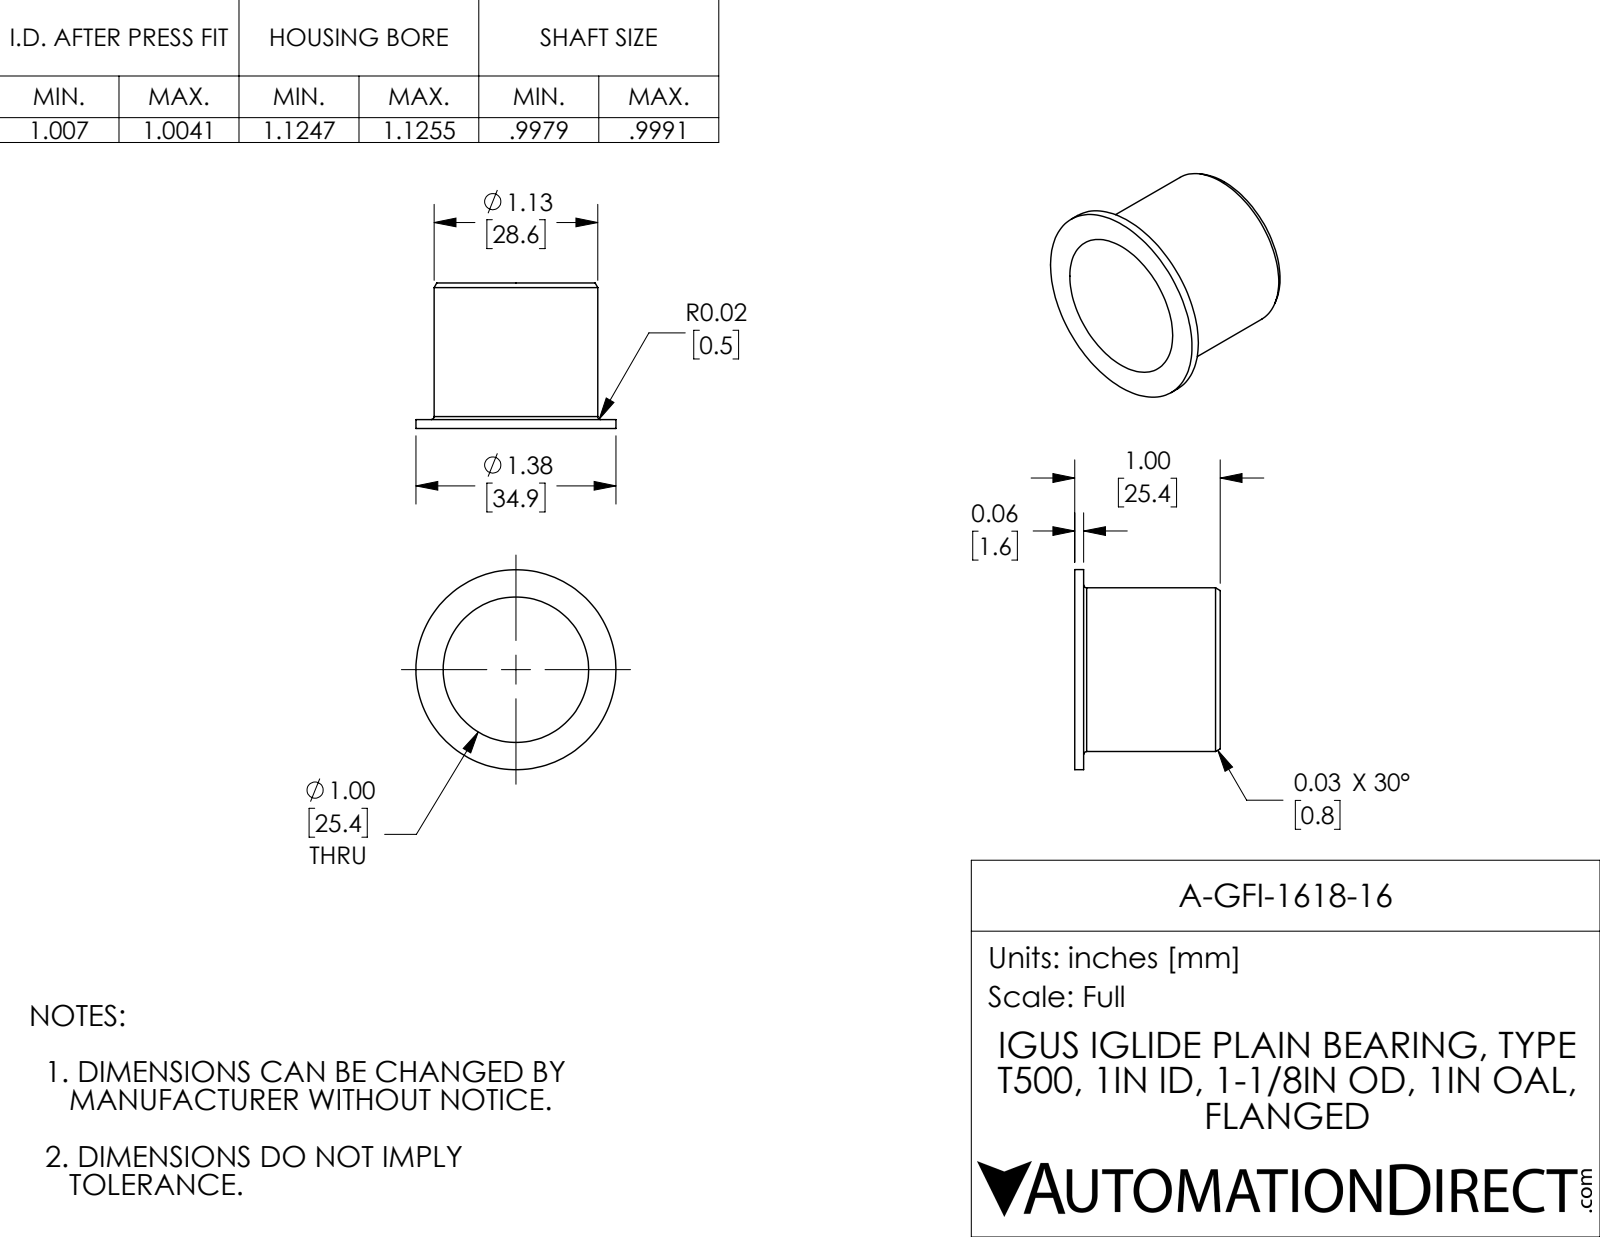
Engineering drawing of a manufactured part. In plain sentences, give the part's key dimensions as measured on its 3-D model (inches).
The part is named "A-GFI-1618-16". Its 3-D file was written by "SolidWorks 2017 (AUTOMOTIVE_DESIGN)". It is 1 solid with 13 faces: 3 planar, 6 cylindrical and 4 other. Overall it measures 1.375 by 1.375 by 1 inches. Its volume is 0.238 cubic inches and its surface area 8.047 square inches. Round holes: 1 of diameter 1. Round bosses or shafts: 1 of diameter 1.375, 1 of diameter 1.125. The main face-to-face distances are 0.062, 1, 0.938.
